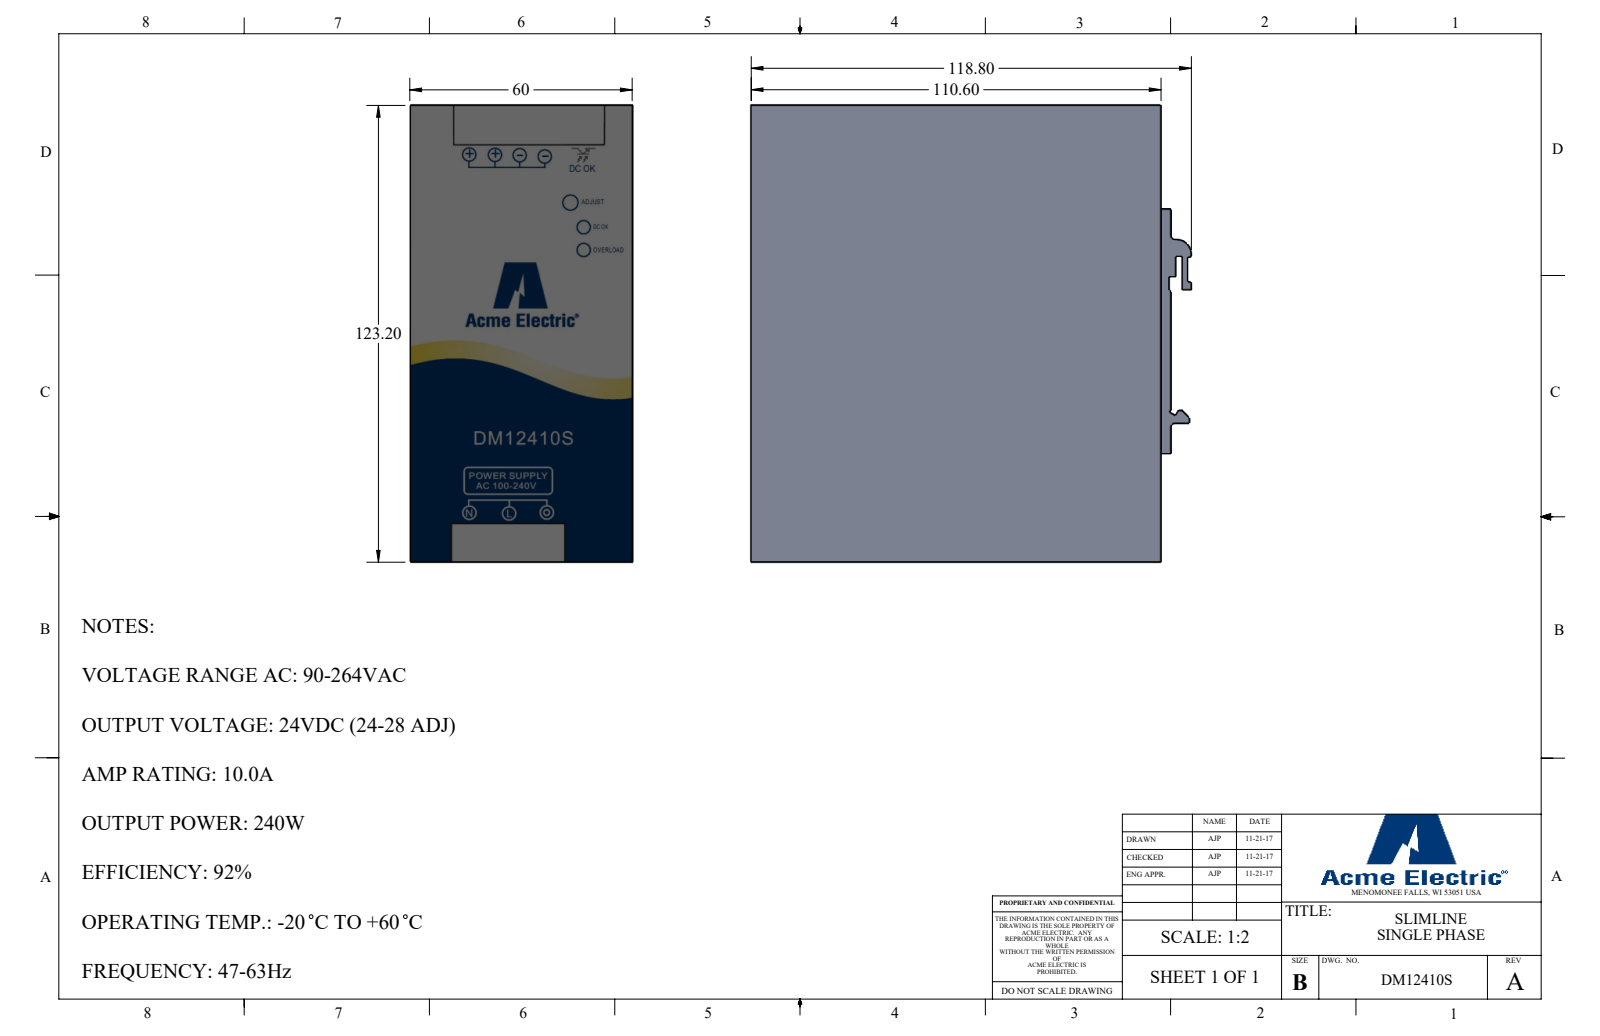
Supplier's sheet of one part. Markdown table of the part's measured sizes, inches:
| quantity | value |
| --- | --- |
| part name | DM12410S |
| STEP written by | SolidWorks 2017 (AUTOMOTIVE_DESIGN) |
| units | inches |
| bodies | 1 solid, 36 faces (33 planar, 3 cylindrical, 0 other) |
| overall size | 4.85 × 4.677 × 2.362 |
| volume | 50.55 in³ |
| surface area | 89.66 in² |
| partial cylindrical surfaces (radius × count) | 0.039 × 2, 0.157 × 1 |
| main face-to-face distances | 2.362, 4.85, 4.354, 0.106, 4.461, 0.276, 2.087, 0.118, 0.224, 4.579 |
